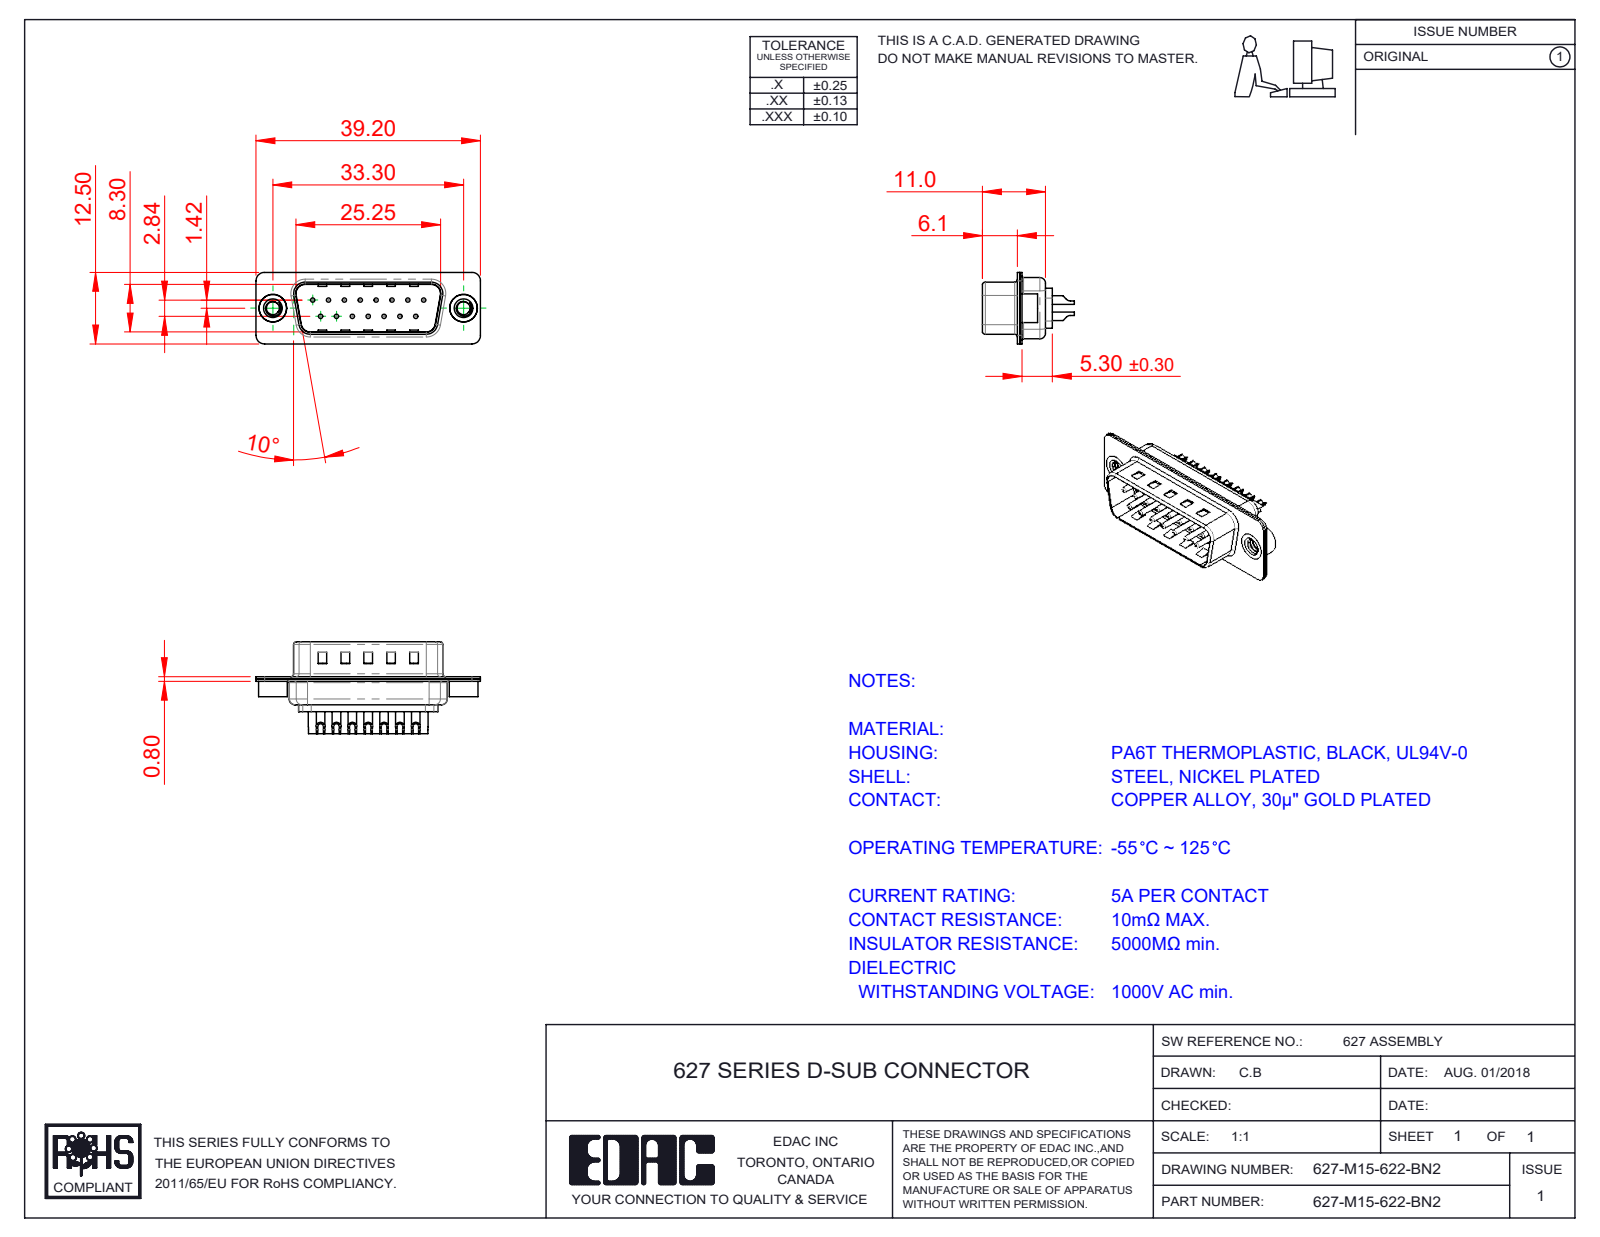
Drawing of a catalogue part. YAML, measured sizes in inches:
part_name: "627M Shell Front_15 Contacts; 627-M15-622-BN2; 627M Contact Row 2_22; 627M Shell Rear_15 Contacts (+3 more)"
step_written_by: "SolidWorks 2020 (CONFIG_CONTROL_DESIGN)"
units: inches
bodies: {solids: 20, faces: 895, planar: 274, cylindrical: 373, other: 248}
overall_size: [1.543, 0.632, 0.492]
volume: 0.115
surface_area: 7.671
round_holes:
  - {diameter: 0.03, count: 15}
  - {diameter: 0.039, count: 15}
  - {diameter: 0.063, count: 15}
  - {diameter: 0.079, count: 15}
  - {diameter: 0.089, count: 2}
  - {diameter: 0.157, count: 2}
  - {diameter: 0.189, count: 2}
round_bosses_or_shafts:
  - {diameter: 0.059, count: 15}
  - {diameter: 0.197, count: 2}
  - {diameter: 0.193, count: 2}
partial_cylinders:
  - {radius: 0.059, count: 16}
  - {radius: 0.079, count: 12}
  - {radius: 0.02, count: 8}
  - {radius: 0.063, count: 8}
  - {radius: 0.039, count: 6}
  - {radius: 0.01, count: 4}
  - {radius: 0.024, count: 4}
  - {radius: 0.026, count: 4}
face_to_face_distances: [0.016, 0.031, 0.374, 0.358, 0.343, 0.39, 0.047, 0.03, 0.014, 0.24]
hole_center_spacings: [0.124, 0.109, 0.218, 0.327, 0.436, 0.198, 0.198, 0.294]
